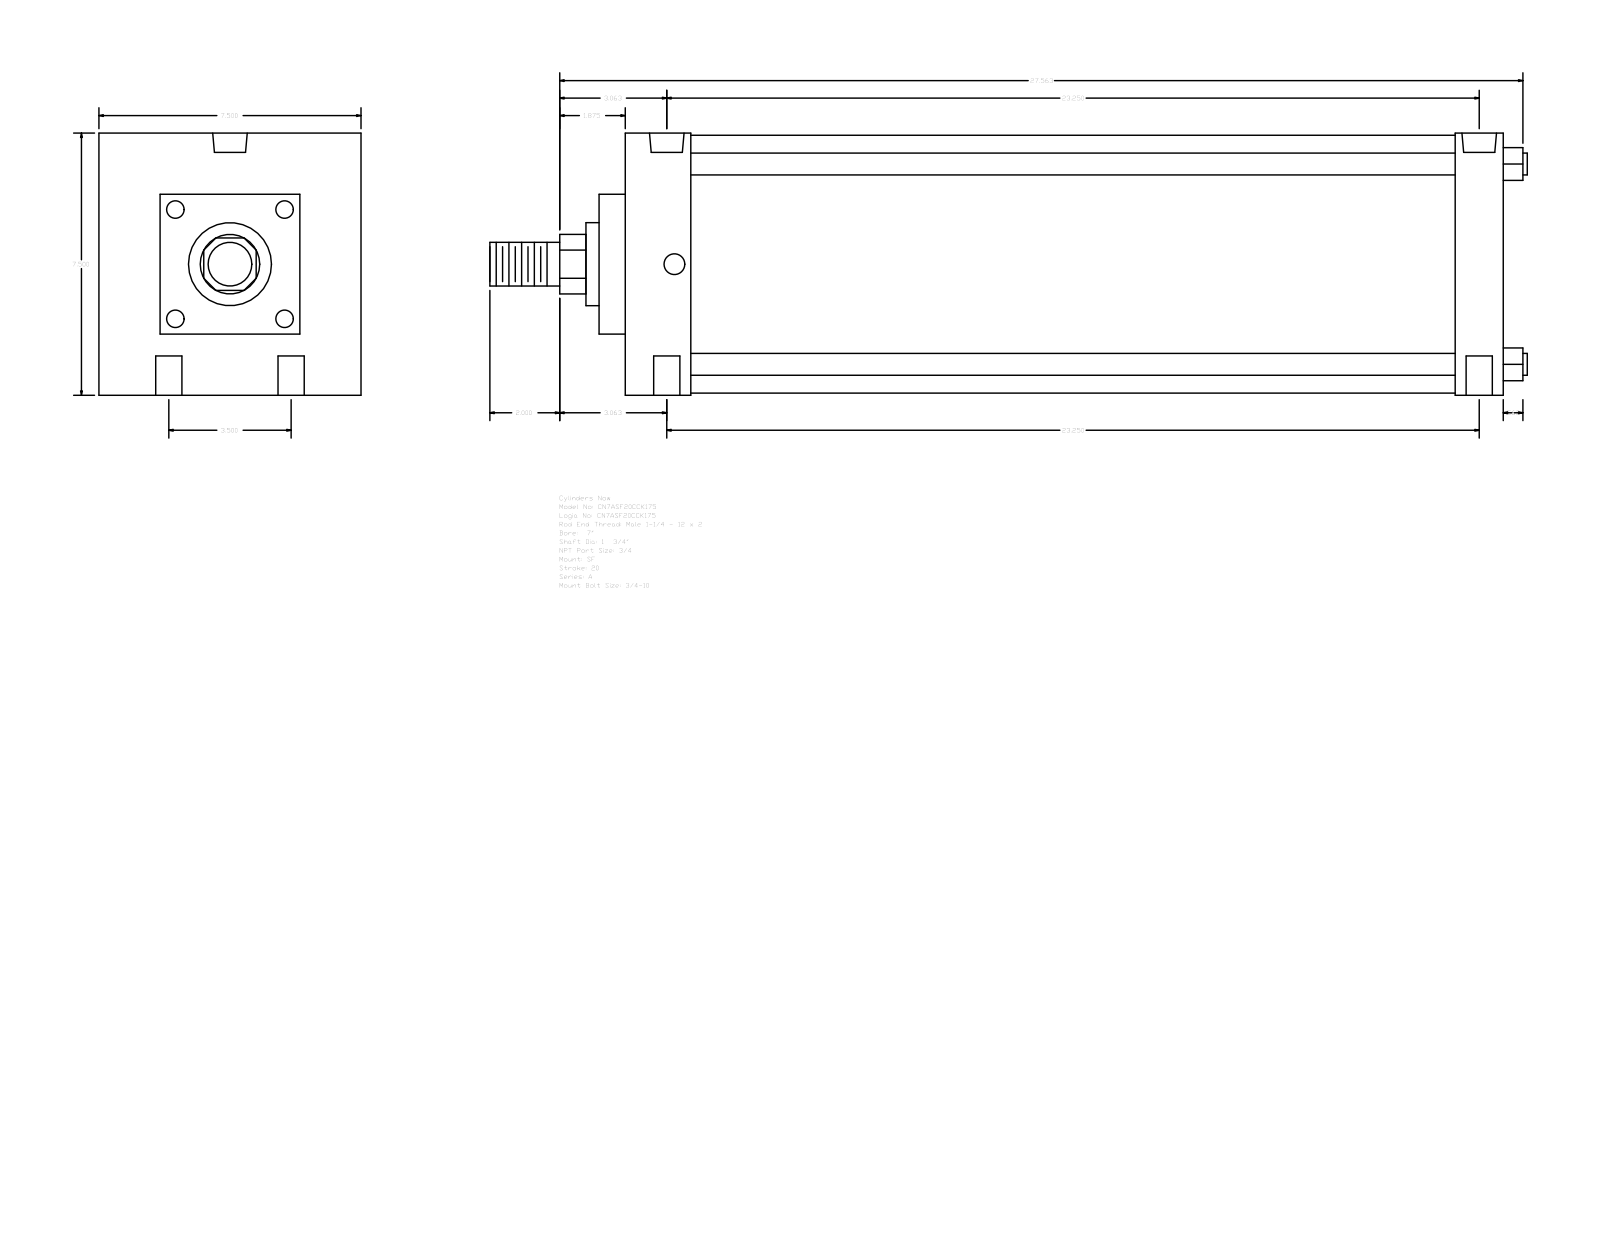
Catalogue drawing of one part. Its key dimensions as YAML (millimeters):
part_name: "A_SF__0700_1.75"
step_written_by: "GSSL Pune (CONFIG_CONTROL_DESIGN)"
units: millimeters
bodies: {solids: 0, faces: 93, planar: 67, cylindrical: 26, other: 0}
overall_size: [754.06, 190.5, 190.5]
round_holes:
  - {diameter: 19.05, count: 4}
  - {diameter: 15.08, count: 2}
  - {diameter: 25.12, count: 2}
round_bosses_or_shafts:
  - {diameter: 15.88, count: 4}
  - {diameter: 187.32, count: 1}
  - {diameter: 60.33, count: 1}
  - {diameter: 44.45, count: 1}
  - {diameter: 31.75, count: 1}
partial_cylinders:
  - {radius: 21.63, count: 1}
face_to_face_distances: [190.5, 638.18, 146.05, 19.05, 47.63, 603.26, 555.63, 590.55, 34.92, 44.45]
hole_center_spacings: [44.45, 592.22, 590.55, 88.9, 597.2, 579.43]
